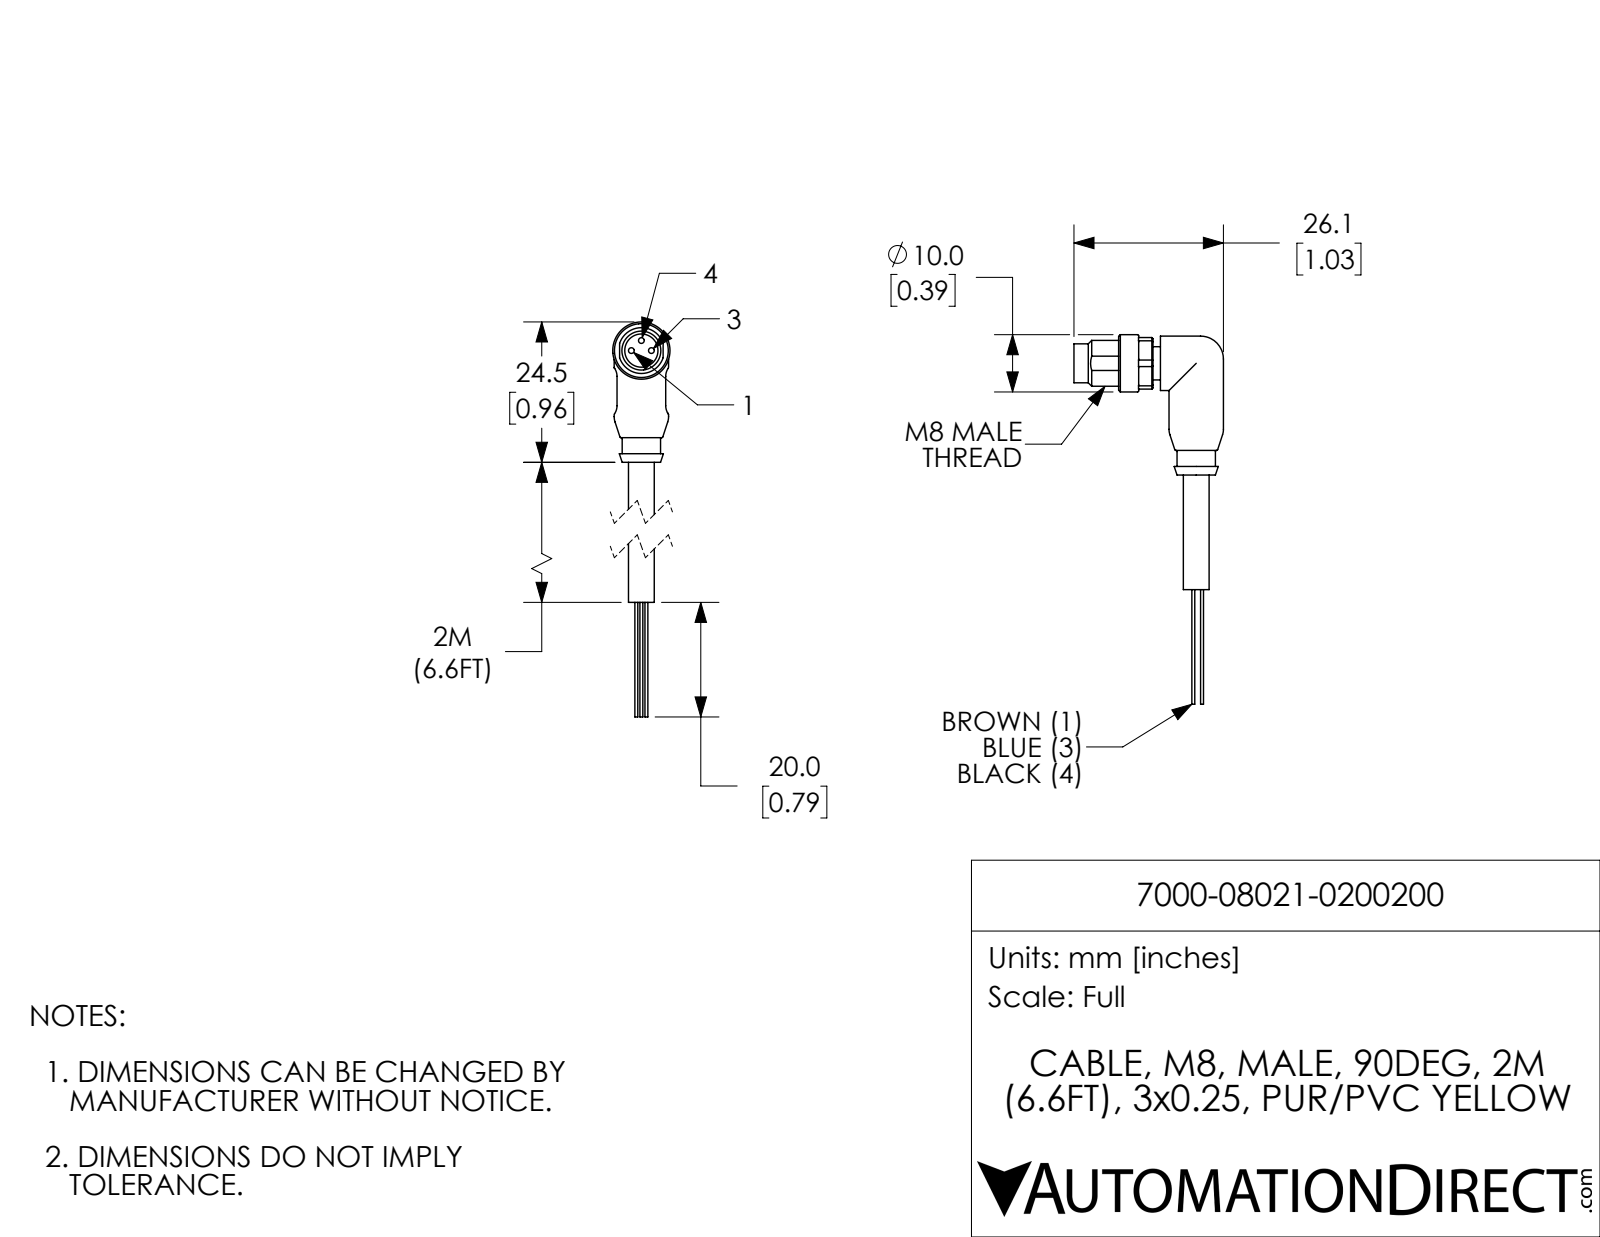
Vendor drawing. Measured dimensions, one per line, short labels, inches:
name: 7000-08021-0200200
written by: SolidWorks 2017 (AUTOMOTIVE_DESIGN)
unit: in
bodies: 4 solids, 118 faces (40 planar, 45 cylindrical, 33 other)
size: 2.539 × 1.028 × 0.394
volume: 0.161 in³; area: 2.831 in²
holes: 1× ⌀0.228
bosses: 3× ⌀0.039, 3× ⌀0.02, 2× ⌀0.374, 1× ⌀0.394, 1× ⌀0.315, 1× ⌀0.268, 1× ⌀0.264, 1× ⌀0.177
rounds: 4× R0.008, 4× R0.098, 1× R0.193
face distances: 0.051, 0.354, 0.018, 0.317, 0.346, 0.398, 0.335, 0.11, 0.236, 0.287
